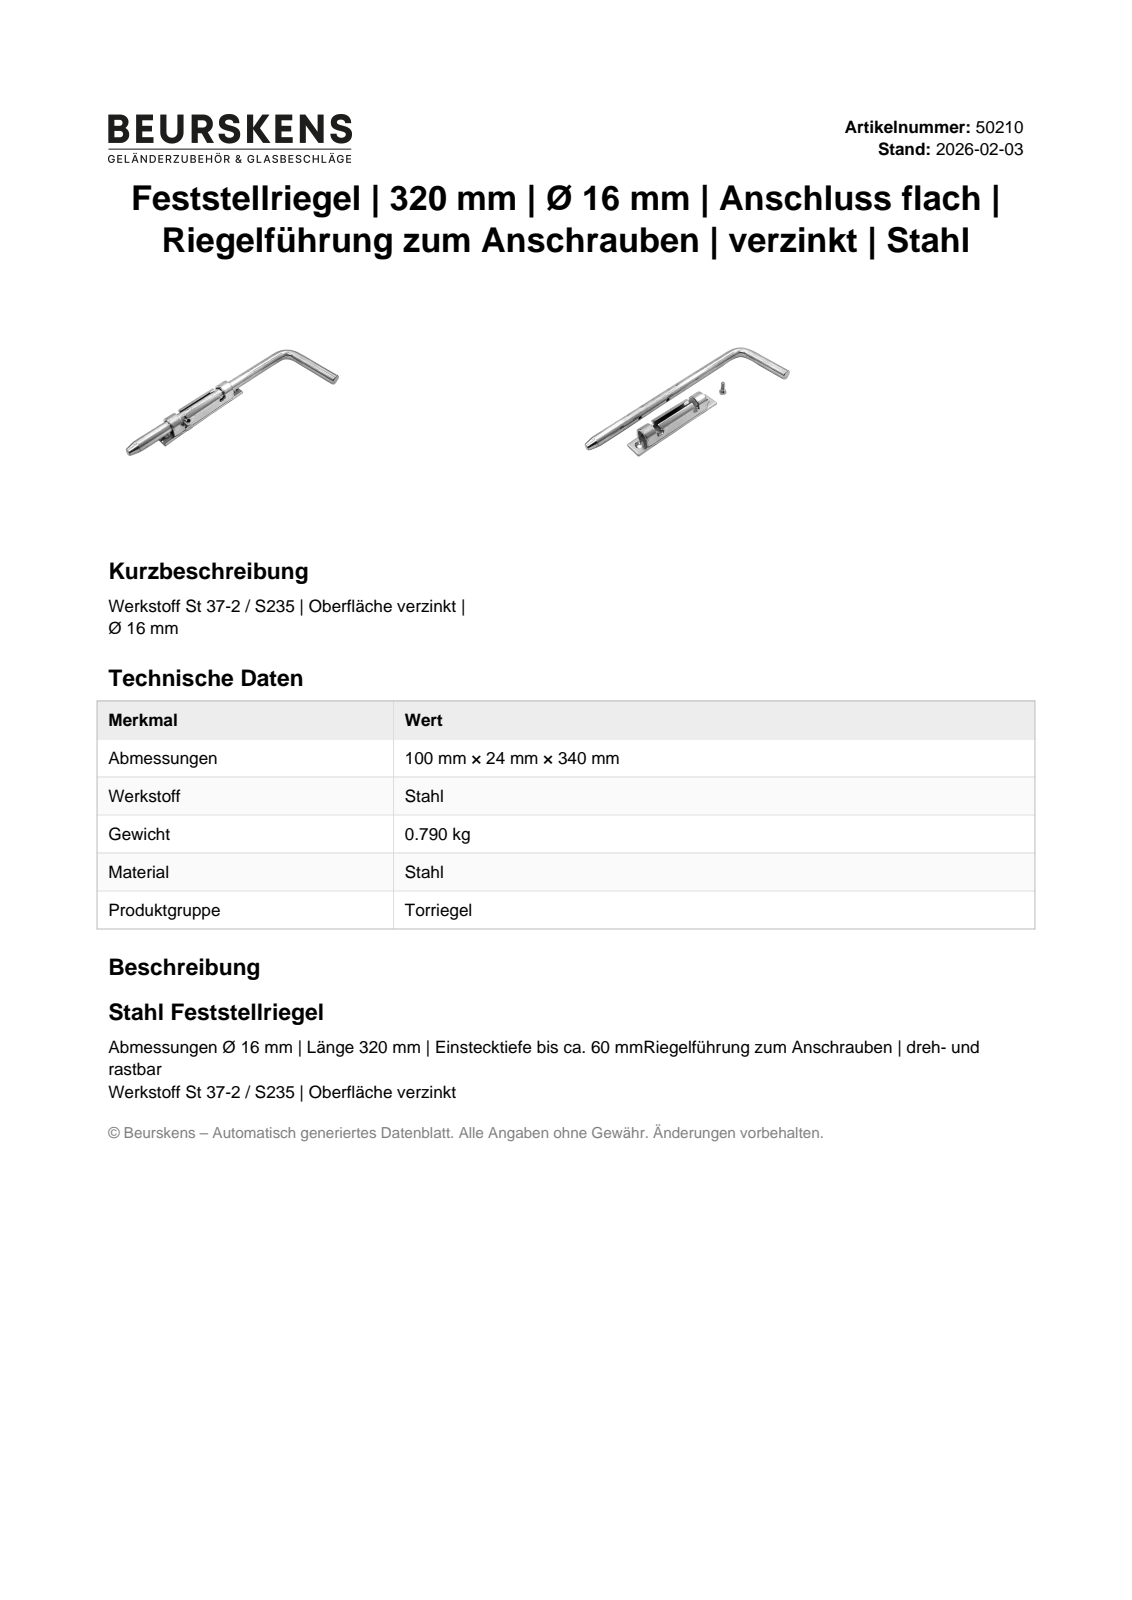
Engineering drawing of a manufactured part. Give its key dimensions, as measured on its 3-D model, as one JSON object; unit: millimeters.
{"part_name": "50210; 50210 Anbauteil; 50210 Riegel; DIN EN ISO 4017 - M6 x 16", "step_written_by": "Autodesk Inventor 2023 (AUTOMOTIVE_DESIGN)", "units": "millimeters", "bodies": {"solids": 3, "faces": 100, "planar": 36, "cylindrical": 36, "other": 28}, "overall_size": [320, 103.66, 27.25], "volume_mm3": 99392, "surface_area_mm2": 38474, "round_holes": [[5.5, 2], [5.8, 2], [8.5, 2]], "round_bosses_or_shafts": [[8.88, 1], [6, 1]], "partial_cylinders_radius": [[0.5, 14], [3.5, 2], [9.75, 1], [11.75, 1]], "face_to_face_distances": [4, 2, 21.5, 23.5, 19.5, 8.25, 6.25, 15.25, 13.25, 80.16], "hole_center_spacings": [26.5, 90.5, 64, 66, 117]}
